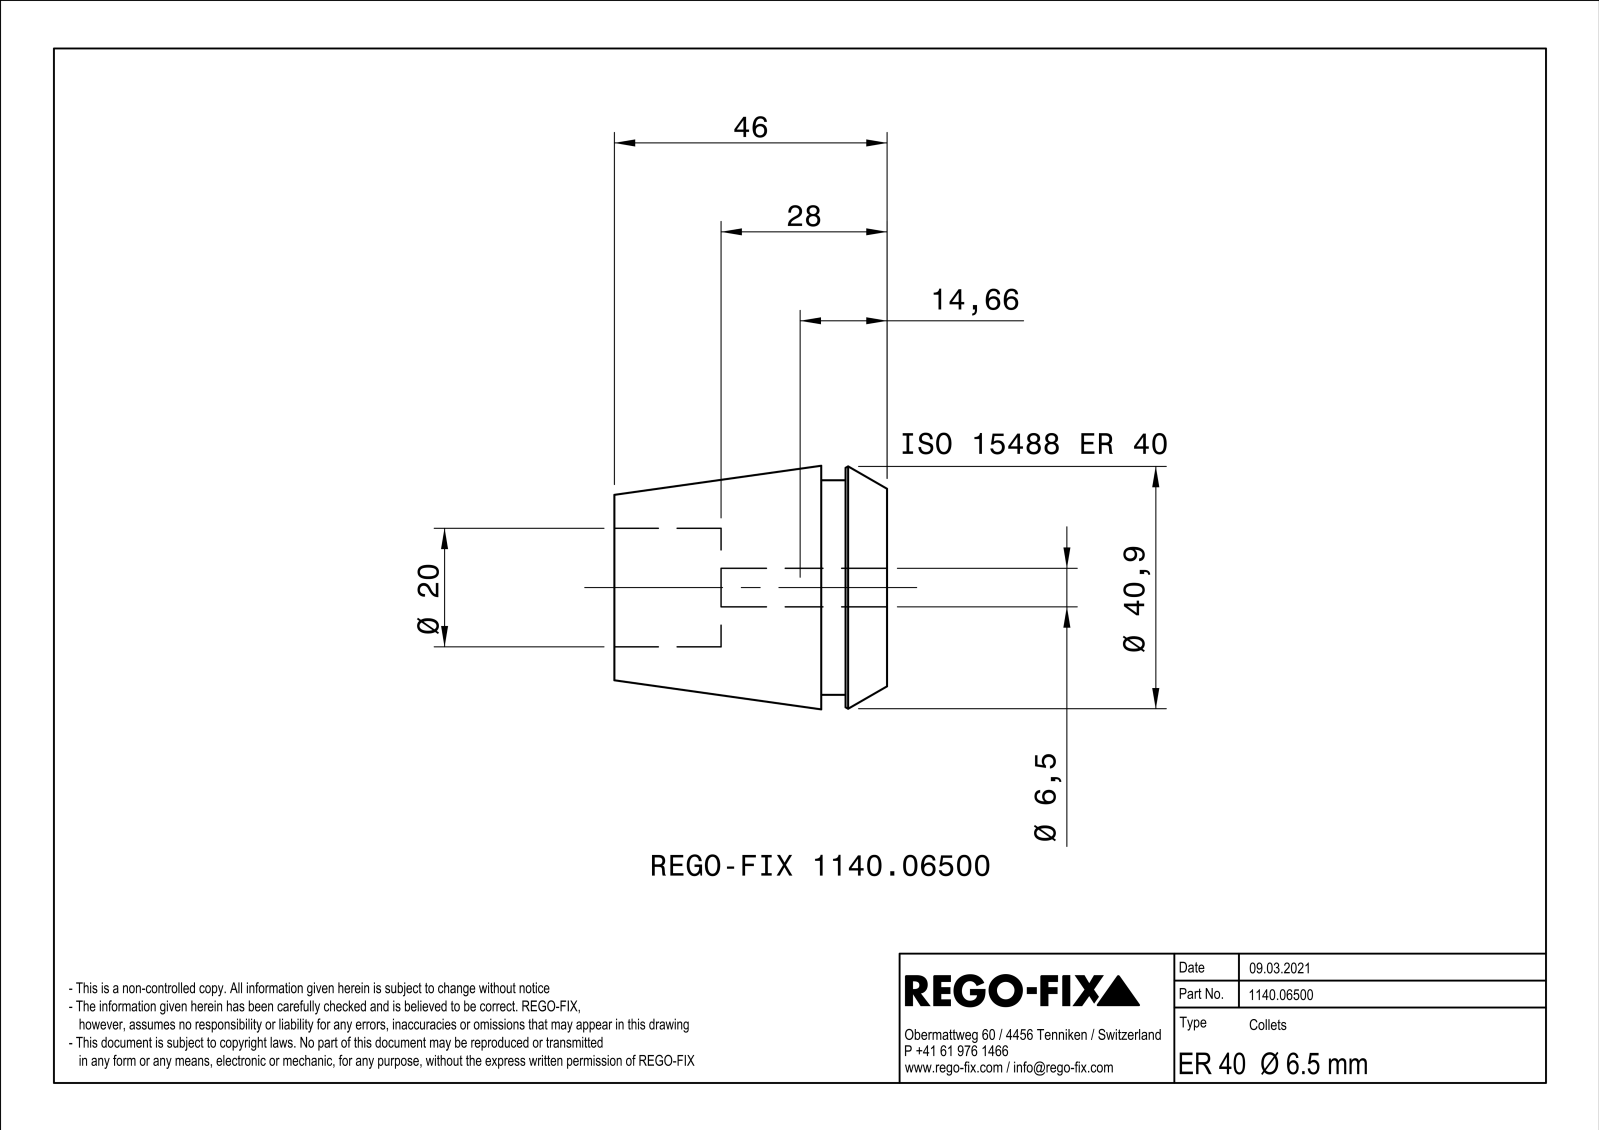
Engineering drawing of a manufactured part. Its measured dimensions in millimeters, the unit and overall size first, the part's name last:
Units: millimetres
Overall size (bounding box): 46 × 40.99 × 40.99
Round holes (diameter × count): ⌀20 ×1
Round bosses / shafts (diameter × count): ⌀36.2 ×1
Partial cylindrical surfaces — rounded edges, fillets, slot ends (radius × count): R45 ×8, R3.25 ×1
Main face-to-face distances: 0.8, 0.78, 0.82, 46, 11.1, 34.9, 7, 4.1, 39, 28
Volume: 36 003 mm³ · Surface area: 21 286 mm²
Bodies: 1 solid, 272 faces (104 planar, 48 cylindrical, 120 other)
Part name (STEP PRODUCT): NOCUT
STEP written by: SIEMENS PLM Software Solid Edge ST10 (AUTOMOTIVE_DESIGN)
